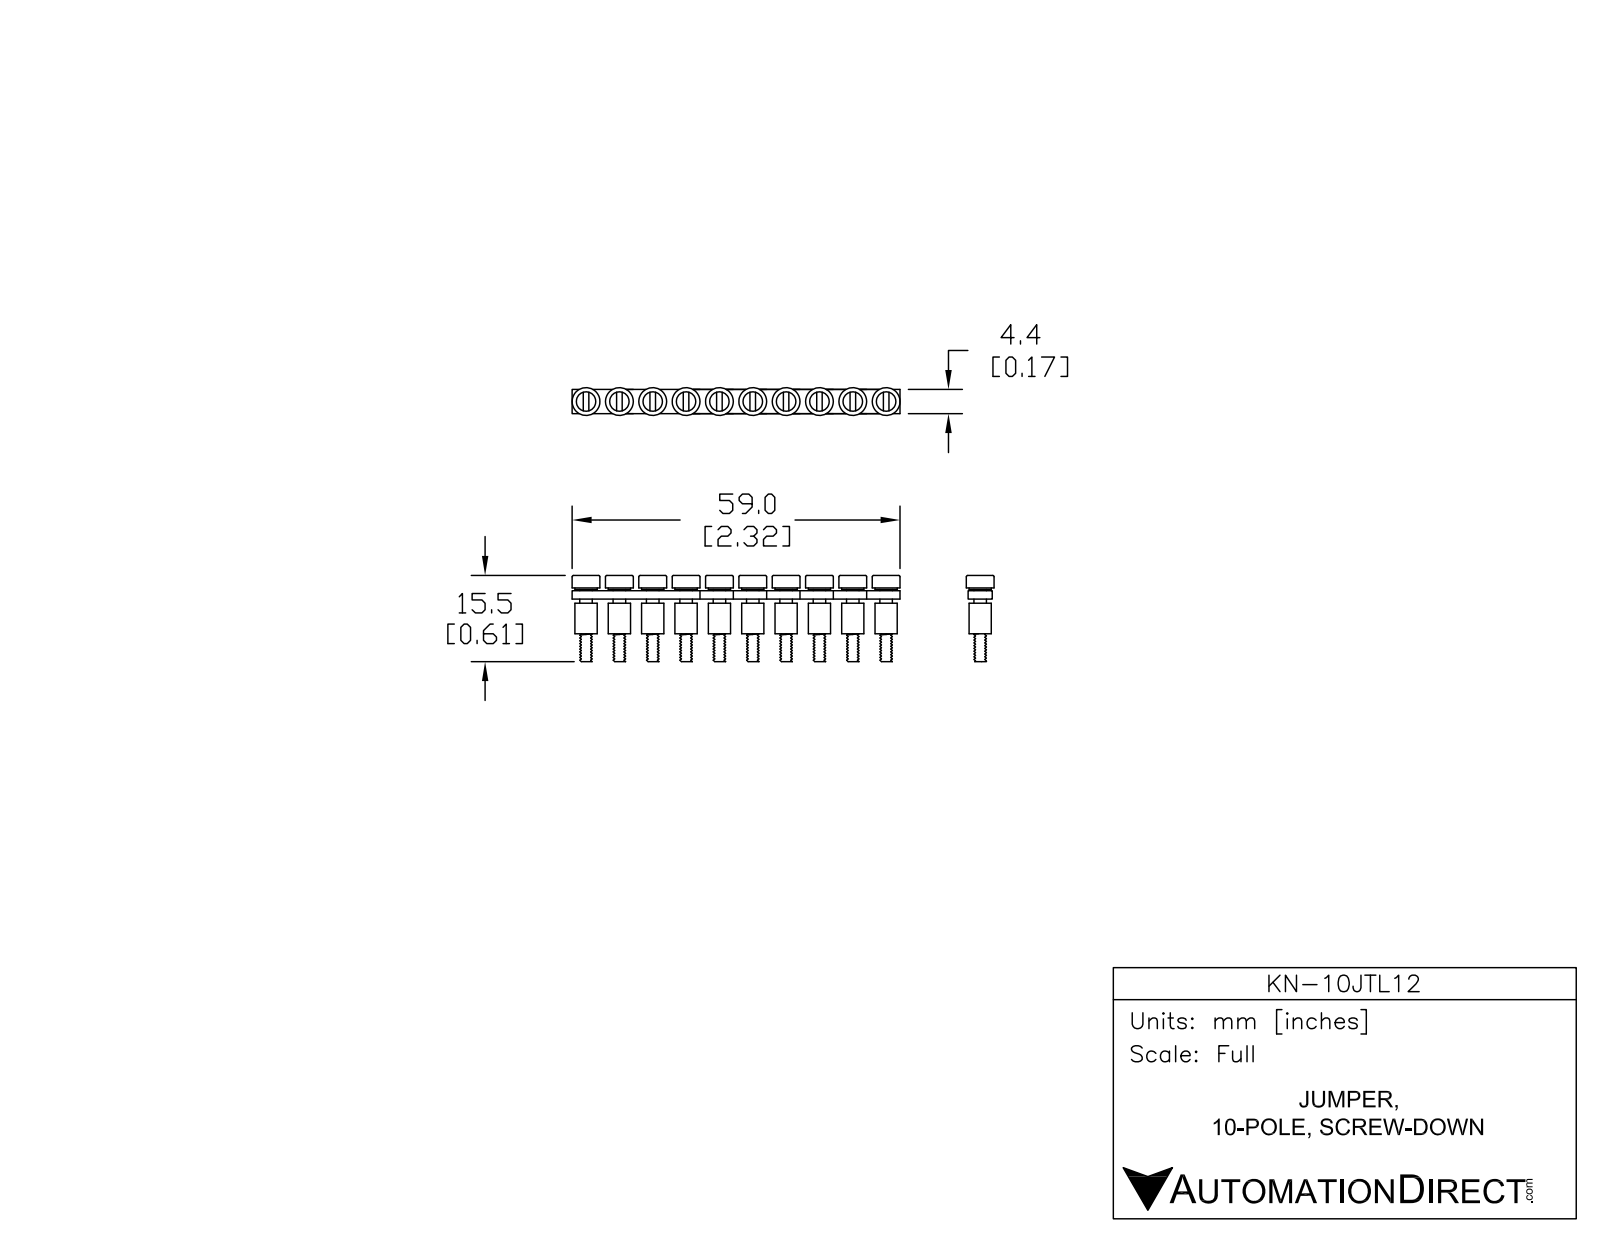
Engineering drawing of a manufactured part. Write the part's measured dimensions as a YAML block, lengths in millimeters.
part_name: "KN-10JTL12"
step_written_by: "SolidWorks 2014 (AUTOMOTIVE_DESIGN)"
units: millimeters
bodies: {solids: 31, faces: 326, planar: 136, cylindrical: 130, other: 60}
overall_size: [59, 15.5, 5]
volume: 1588
surface_area: 4374
round_holes:
  - {diameter: 3, count: 10}
  - {diameter: 3.5, count: 10}
round_bosses_or_shafts:
  - {diameter: 5, count: 10}
  - {diameter: 4, count: 10}
  - {diameter: 2.25, count: 10}
face_to_face_distances: [1.5, 2.25, 2, 1.75, 0.5, 2.75, 2.5, 5, 1, 0.75]
hole_center_spacings: [6, 12, 18, 24, 30, 36, 42, 48]
